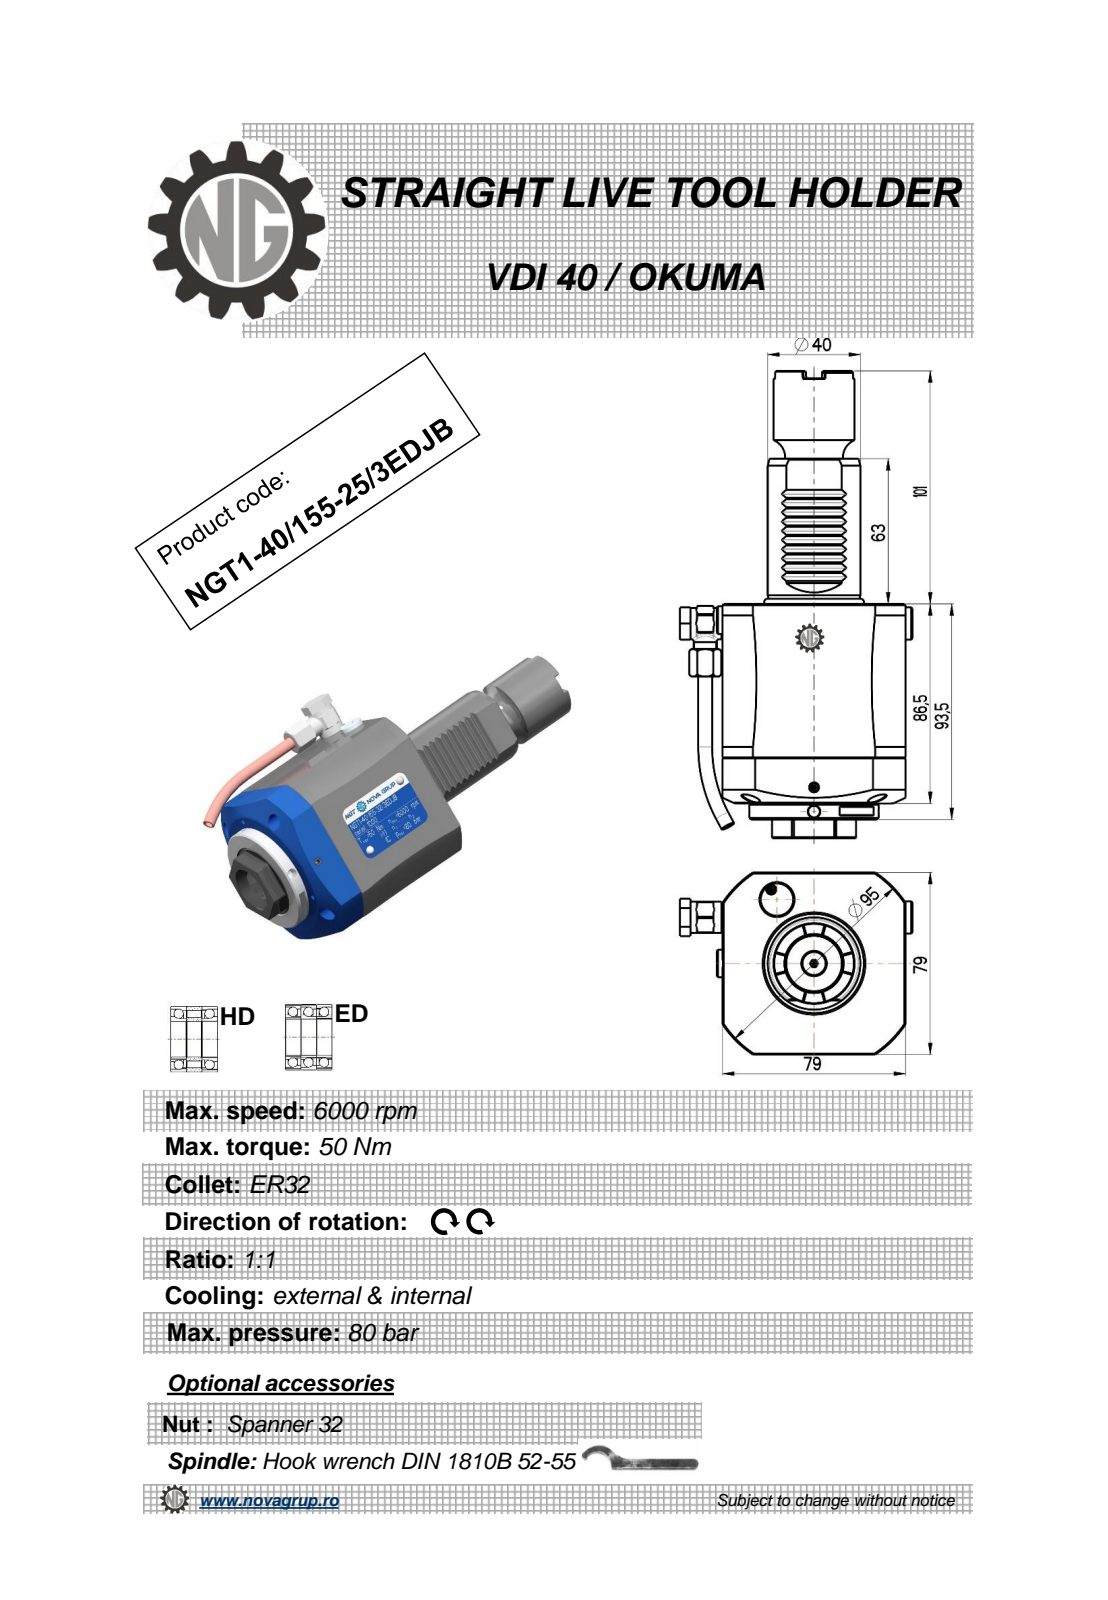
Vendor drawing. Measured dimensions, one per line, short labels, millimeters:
name: NGT1_40_155_32_3HDJB
written by: PRO/ENGINEER BY PARAMETRIC TECHNOLOGY CORPORATION, 2010280 (CONFIG_CONTROL_DESIGN)
unit: mm
bodies: 2 solids, 426 faces (168 planar, 101 cylindrical, 157 other)
size: 202.5 × 100.4 × 79
volume: 631 595 mm³; area: 58 595 mm²
holes: 3× ⌀4, 2× ⌀5, 1× ⌀3, 1× ⌀6, 1× ⌀6.2, 1× ⌀9, 1× ⌀10, 1× ⌀11, 1× ⌀23, 1× ⌀25
bosses: 1× ⌀56, 1× ⌀40, 1× ⌀35, 1× ⌀14, 1× ⌀13.6, 1× ⌀13, 1× ⌀12, 1× ⌀10
rounds: 10× R0.3, 6× R0.41, 4× R0.5, 1× R7.7, 1× R47, 1× R47.5
face distances: 79, 86.5, 7, 93.5, 2.83, 23.5, 55.5, 156.5, 149.5, 63
hole spacings: 0.4, 51.08, 51.45, 83.92
